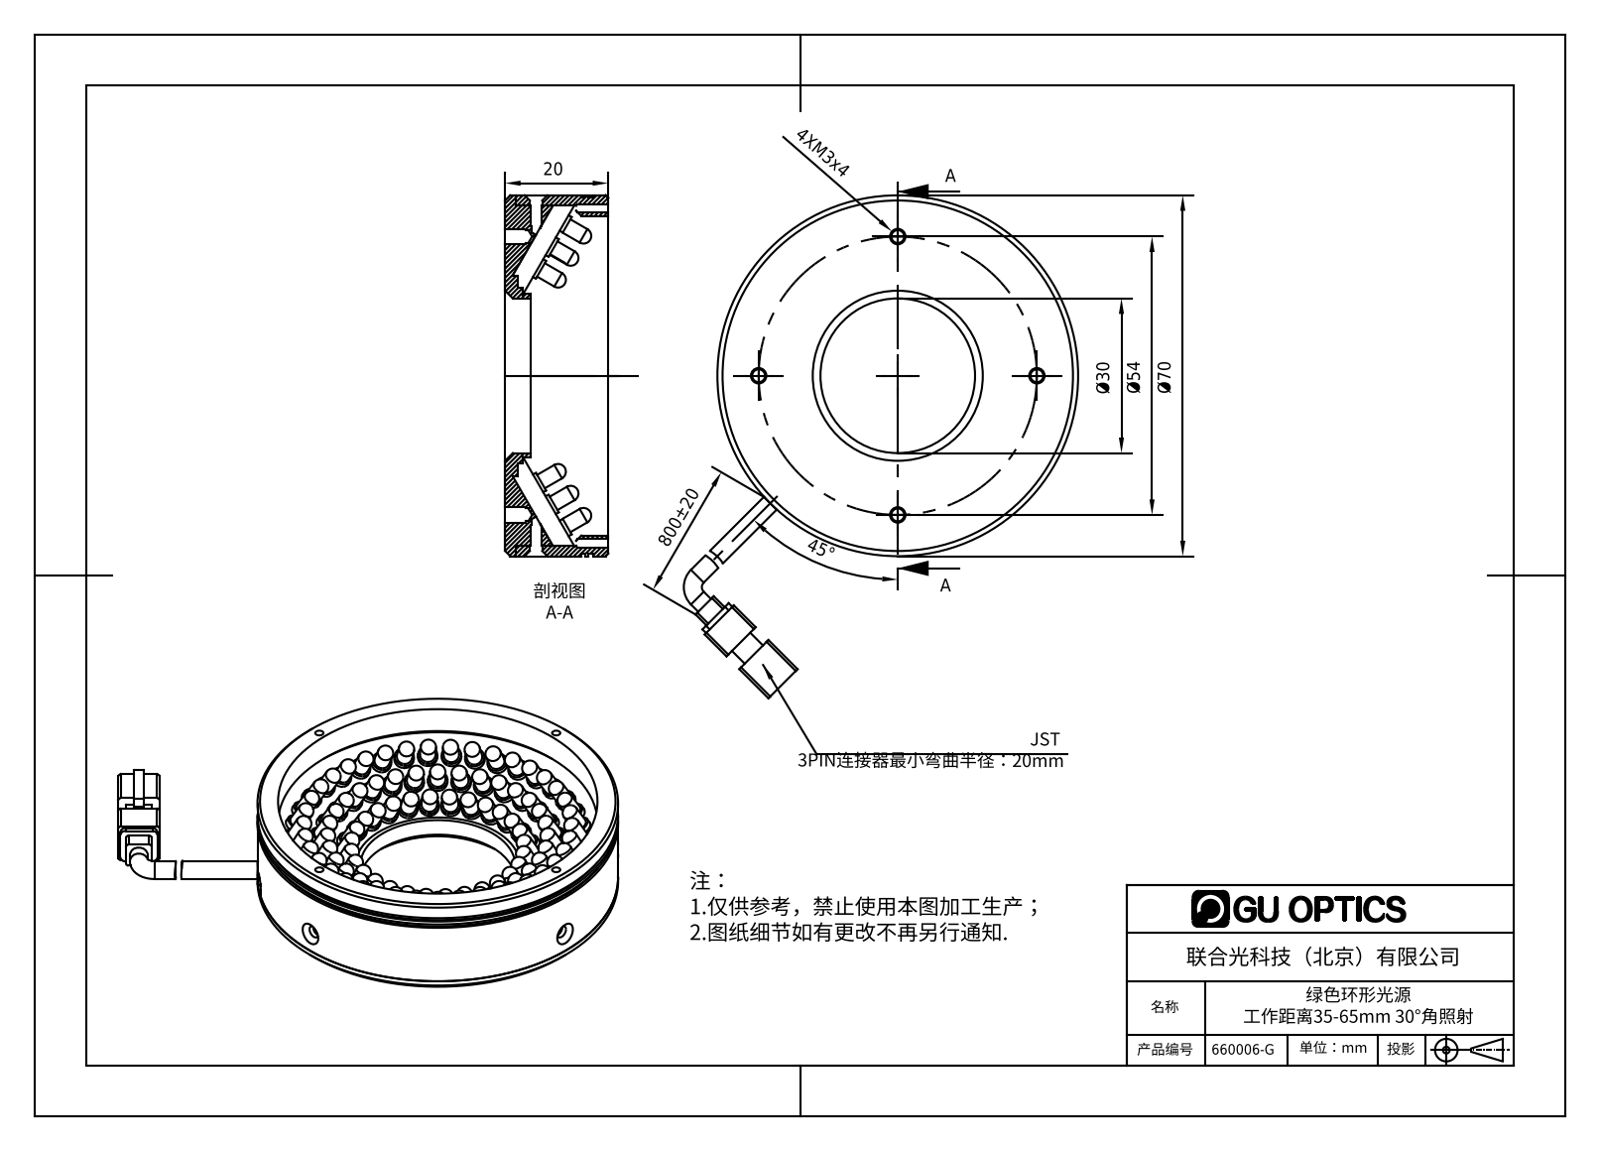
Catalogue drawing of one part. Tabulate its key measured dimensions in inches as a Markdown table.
| quantity | value |
| --- | --- |
| part name | 660006-G |
| STEP written by | SolidWorks 2016 (AUTOMOTIVE_DESIGN) |
| units | inches |
| bodies | 103 solids, 1954 faces (1269 planar, 520 cylindrical, 165 other) |
| overall size | 3.842 × 3.013 × 0.799 |
| volume | 1.824 in³ |
| surface area | 53.82 in² |
| round holes (diameter × count) | 0.118 × 7, 0.063 × 6, 0.098 × 4, 0.079 × 2, 0.094 × 2, 1.181 × 1, 2.441 × 1 |
| round bosses / shafts (diameter × count) | 0.15 × 98, 0.118 × 96, 0.138 × 2, 2.756 × 1, 2.717 × 1, 2.598 × 1, 1.529 × 1, 1.339 × 1 |
| partial cylindrical surfaces (radius × count) | 0.02 × 8, 0.063 × 6, 0.039 × 4, 0.354 × 1 |
| main face-to-face distances | 0.079, 0.787, 0.709, 0.039, 0.02, 0.059, 0.118, 0.096, 0.017, 0.691 |
| hole center spacings | 1.663, 0.217, 1.063, 1.28, 1.503, 1.809, 2.343, 2.126 |
